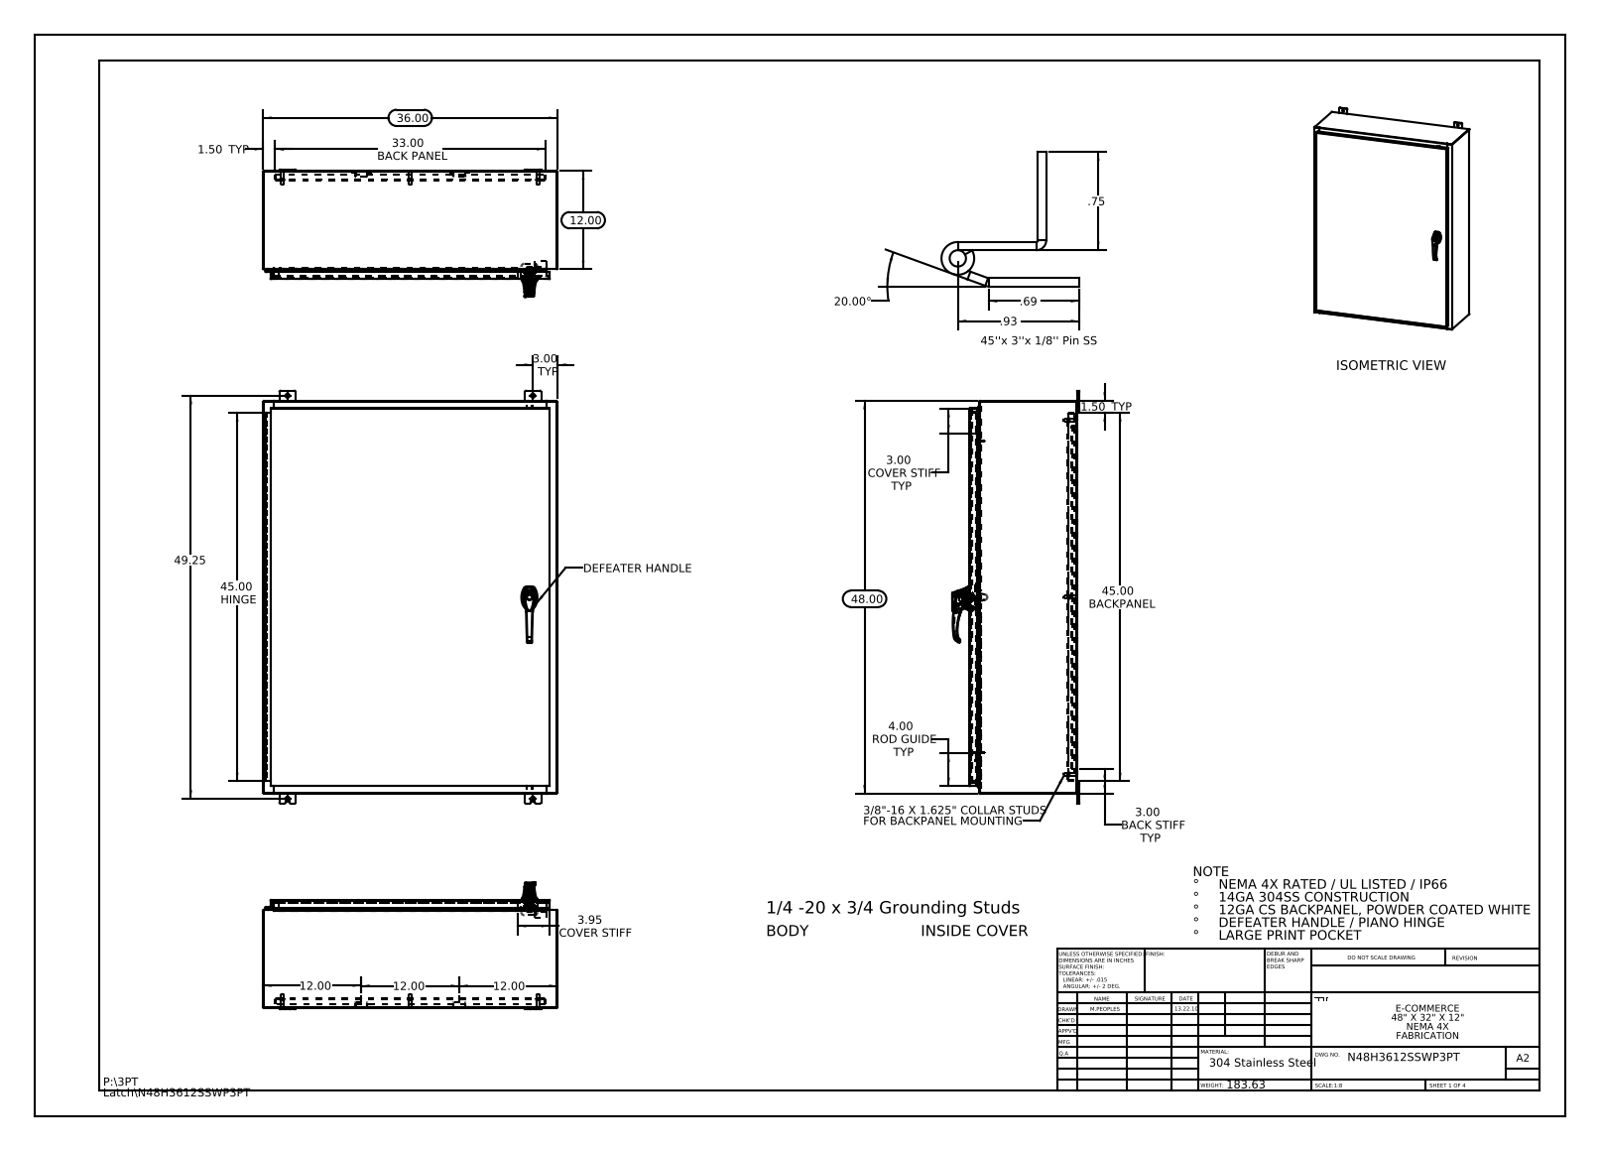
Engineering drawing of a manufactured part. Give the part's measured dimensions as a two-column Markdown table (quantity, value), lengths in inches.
| quantity | value |
| --- | --- |
| part name | N48H3612SSWP3PT Mounting Studs; 022151; 012103_012102; 00005090 (+8 more) |
| STEP written by | SolidWorks 2013 (CONFIG_CONTROL_DESIGN) |
| units | inches |
| bodies | 39 solids, 3224 faces (1273 planar, 1257 cylindrical, 694 other) |
| overall size | 50.5 × 36 × 15.495 |
| volume | 656 in³ |
| surface area | 16 305 in² |
| round holes (diameter × count) | 0.5 × 12, 0.25 × 10, 0.138 × 3, 0.161 × 3, 0.079 × 2, 0.203 × 2, 0.313 × 2, 0.437 × 2, 0.125 × 1, 0.125 × 1, 0.197 × 1, 0.276 × 1 |
| round bosses / shafts (diameter × count) | 0.625 × 8, 0.375 × 8, 0.33 × 8, 1.181 × 1, 0.748 × 1, 0.68 × 1, 0.661 × 1, 0.639 × 1 |
| partial cylindrical surfaces (radius × count) | 0.118 × 37, 0.013 × 34, 0.006 × 33, 0.088 × 28, 0.19 × 24, 0.039 × 15, 0.028 × 12, 0.008 × 6 |
| main face-to-face distances | 0.075, 13.126, 13.051, 13.201, 0.104, 1, 12.126, 1.075, 12.051, 1.179 |
| hole center spacings | 17.357, 19.665, 21.625, 38.003, 45.986, 31.25, 43.25, 0.295 |
